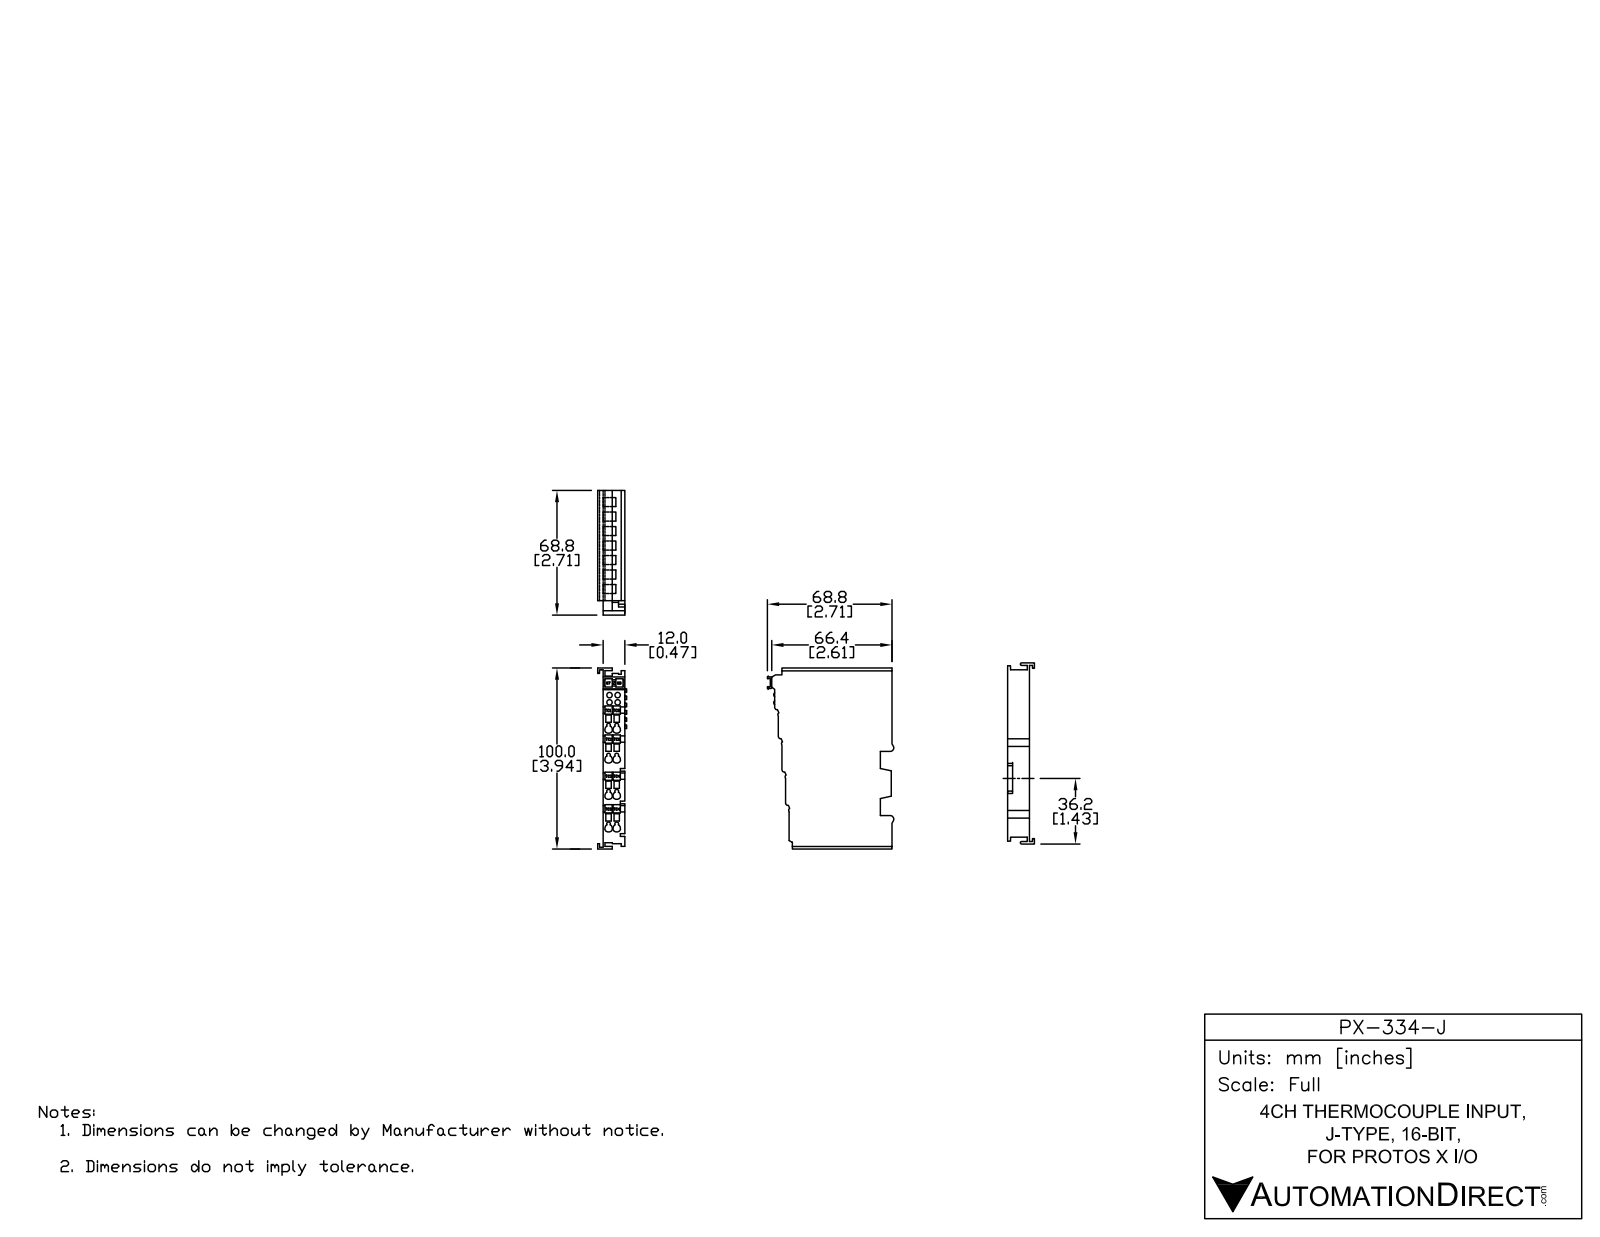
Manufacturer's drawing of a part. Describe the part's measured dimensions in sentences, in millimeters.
The part is named "PX-334-J". Its 3-D file was written by "SolidWorks 2014 (AUTOMOTIVE_DESIGN)". It is 28 solids with 1367 faces: 963 planar, 344 cylindrical and 60 other. Overall it measures 100.25 by 71.26 by 15.15 millimeters. Its volume is 58 403 cubic millimeters and its surface area 33 884 square millimeters. Round holes: 8 of diameter 4, 4 of diameter 3.5. Partial cylindrical surfaces (rounded edges, fillets, slot ends): 46 of radius 0.3, 35 of radius 0.25, 12 of radius 0.38, 10 of radius 0.12, 9 of radius 1, 8 of radius 0.4, 4 of radius 0.17, 4 of radius 1.03. The main face-to-face distances are 12, 1, 2, 10, 1.85, 11, 8.7, 4, 3.15, 1.22. The hole center spacings are 4.5, 5, 18.4, 19.07, 6.36, 16, 16.76, 20.41.
